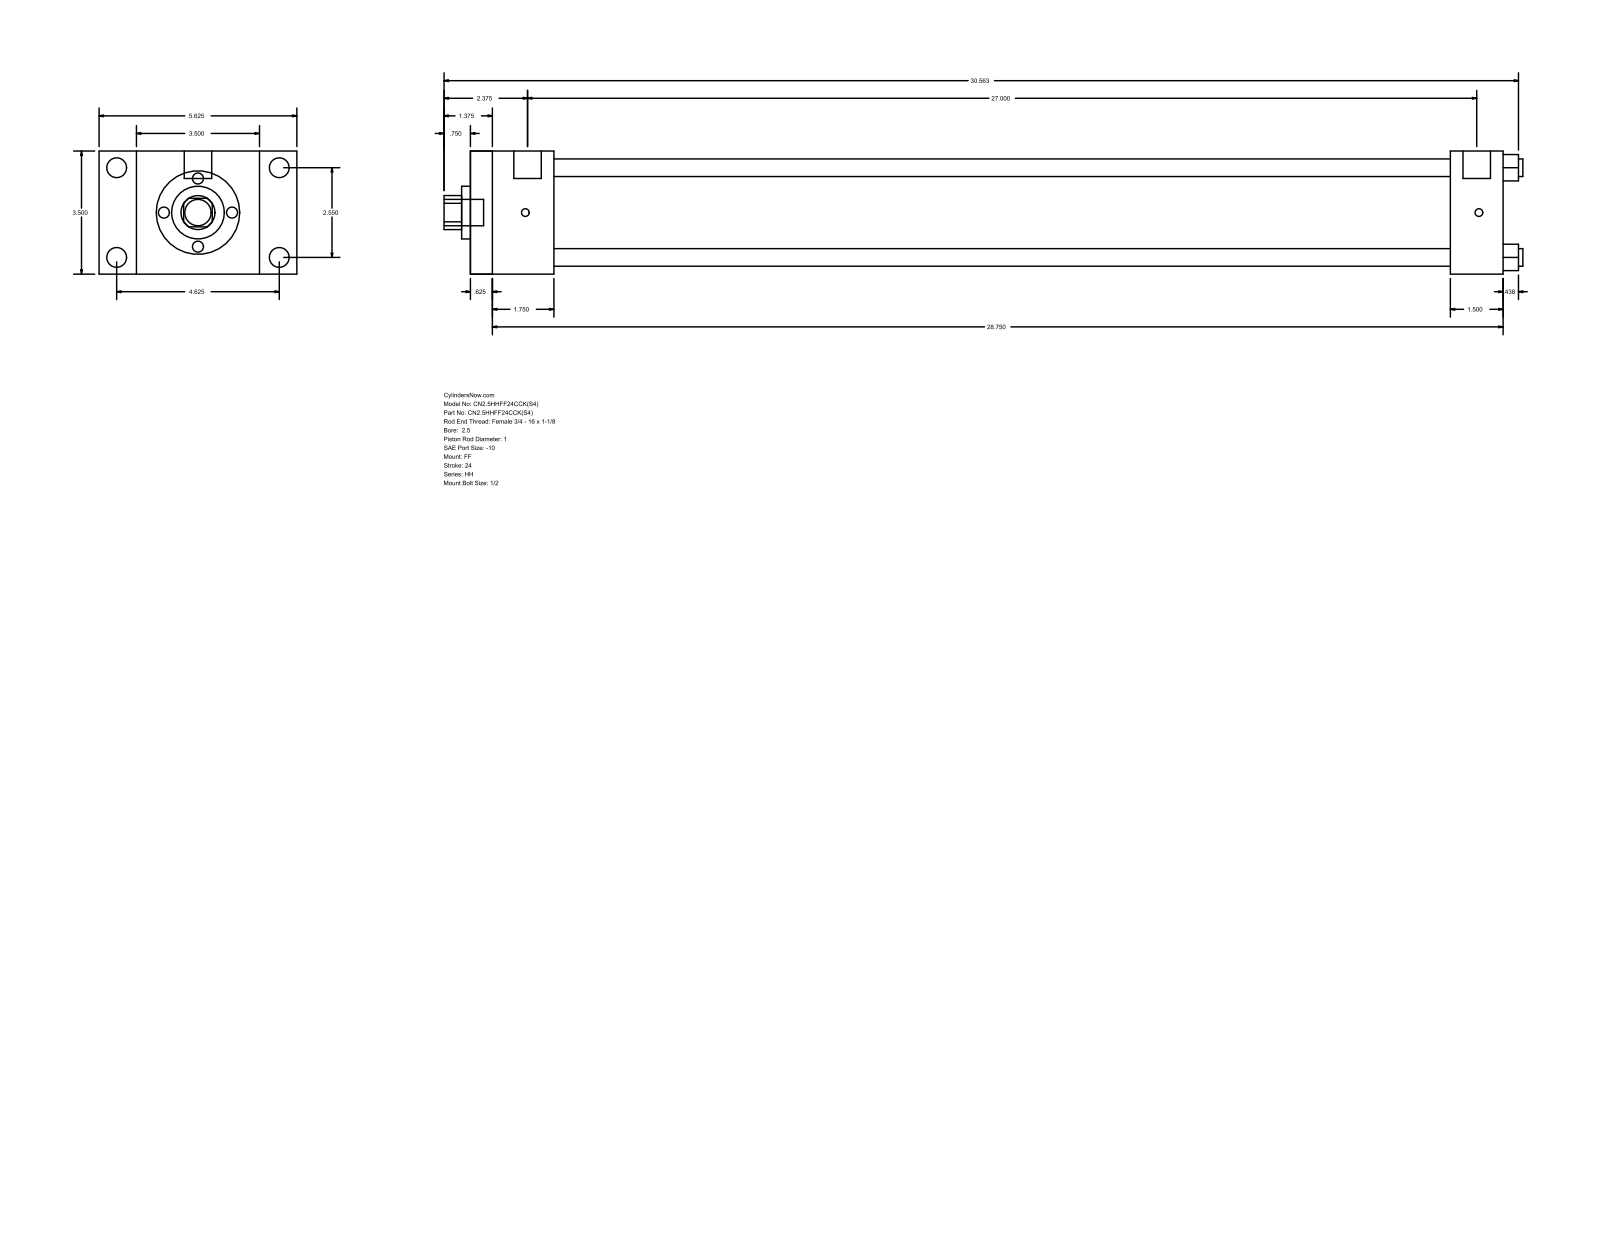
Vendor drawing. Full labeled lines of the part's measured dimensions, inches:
Part name (STEP PRODUCT): HH_FF__0250_1
STEP written by: GSSL Pune (CONFIG_CONTROL_DESIGN)
Units: inches
Bodies: 0 solids, 92 faces (64 planar, 28 cylindrical, 0 other)
Overall size (bounding box): 30.687 × 5.625 × 3.5
Round holes (diameter × count): ⌀0.5 ×4, ⌀1 ×1, ⌀1.5 ×1, ⌀2.875 ×1
Round bosses / shafts (diameter × count): ⌀0.563 ×4, ⌀0.219 ×4, ⌀0.781 ×2, ⌀0.75 ×1
Partial cylindrical surfaces — rounded edges, fillets, slot ends (radius × count): R0.484 ×1
Main face-to-face distances: 3.5, 29.375, 0.625, 28.75, 2.375, 1.75, 27, 27.875, 27.25, 25.5
Hole centre spacings: 1.803, 2.55, 3.606
